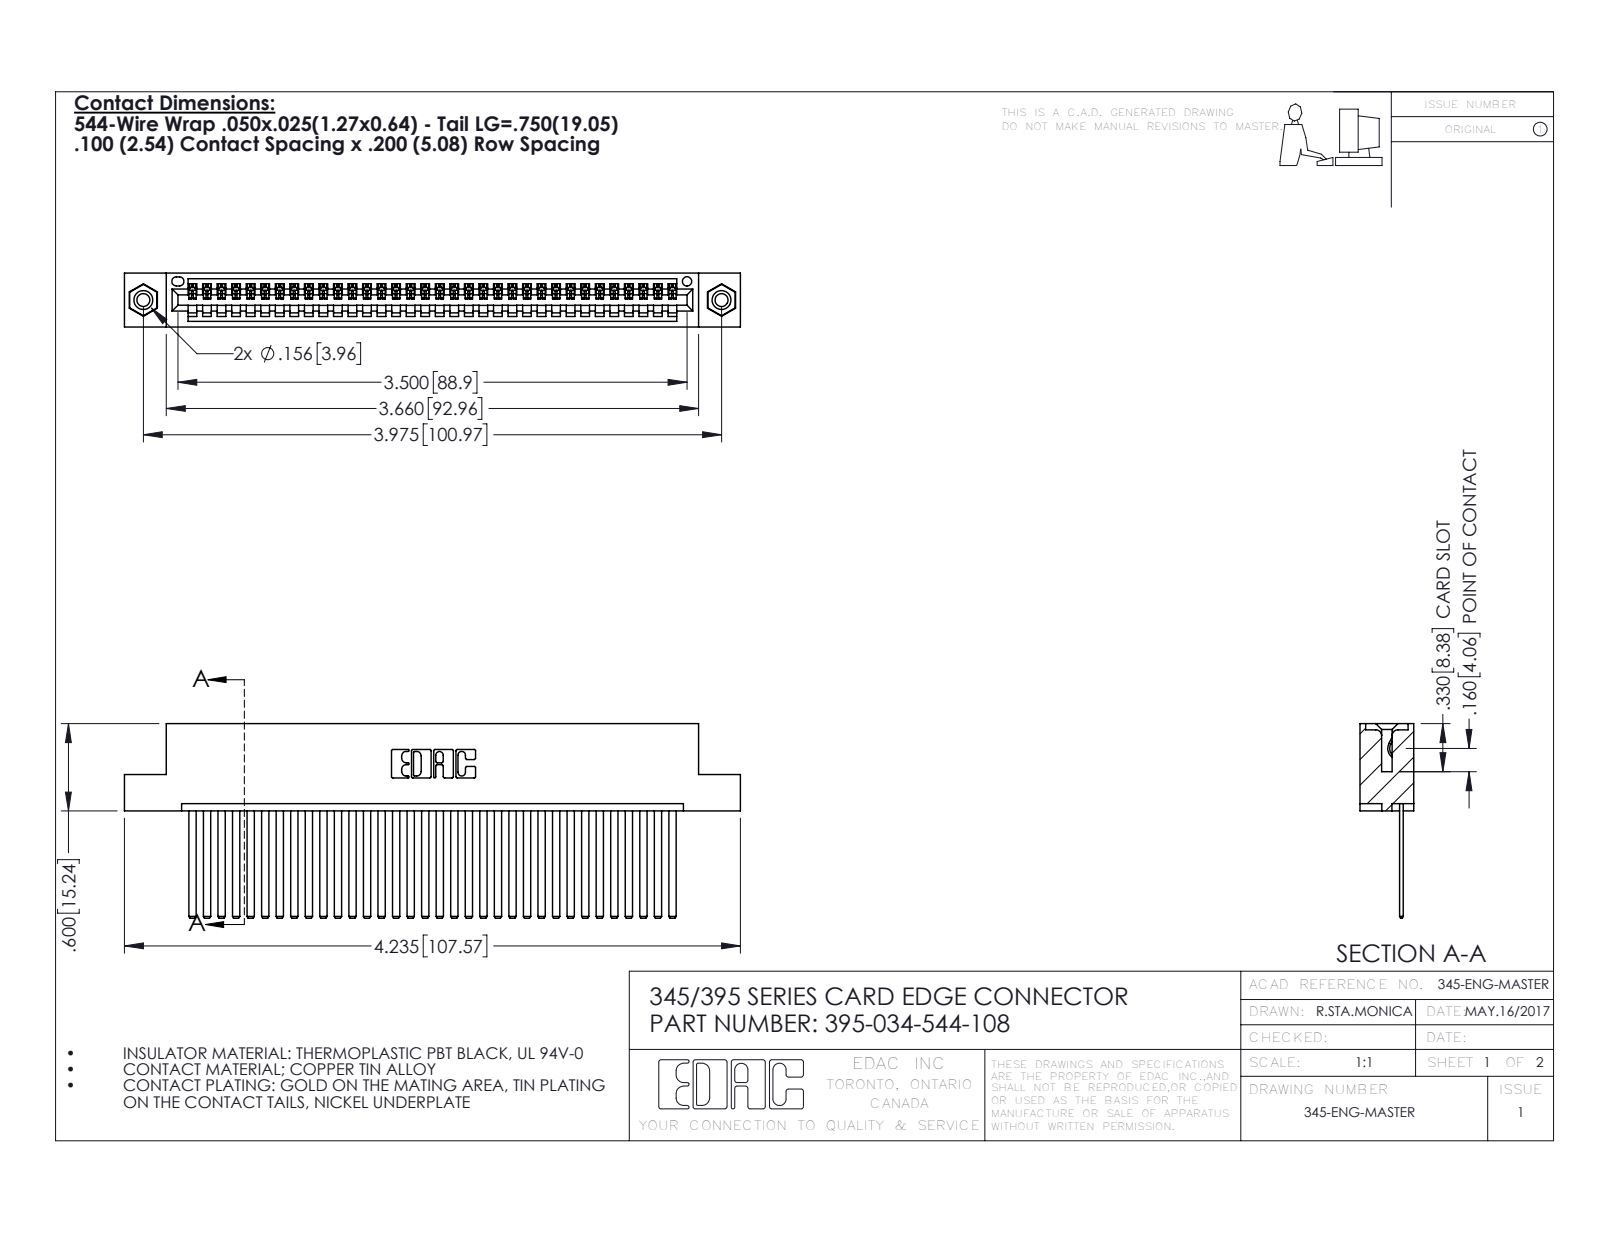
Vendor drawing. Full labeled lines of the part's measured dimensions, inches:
Part name (STEP PRODUCT): 395-034-544-108; 345-250-001_345-250-003-102; 345-292-001_345-293-144; 345 Part_Flush Mounting Lugs - 0.156 Dia-TI
STEP written by: SolidWorks 2016 (CONFIG_CONTROL_DESIGN)
Units: inches
Bodies: 37 solids, 1954 faces (1336 planar, 602 cylindrical, 16 other)
Overall size (bounding box): 4.235 × 1.337 × 0.37
Volume: 0.643 in³ · Surface area: 23.4 in²
Round holes (diameter × count): ⌀0.089 ×2, ⌀0.125 ×2, ⌀0.156 ×2, ⌀0.064 ×1
Round bosses / shafts (diameter × count): ⌀0.155 ×2
Partial cylindrical surfaces — rounded edges, fillets, slot ends (radius × count): R0.006 ×68, R0.01 ×22, R0.007 ×6, R0.031 ×6, R0.026 ×3, R0.031 ×2, R0.04 ×2, R0.014 ×1
Main face-to-face distances: 0.072, 0.298, 0.025, 0.098, 0.272, 0.2, 0.37, 0.225, 0.149, 0.072
Hole centre spacings: 0.27, 3.74, 3.975
